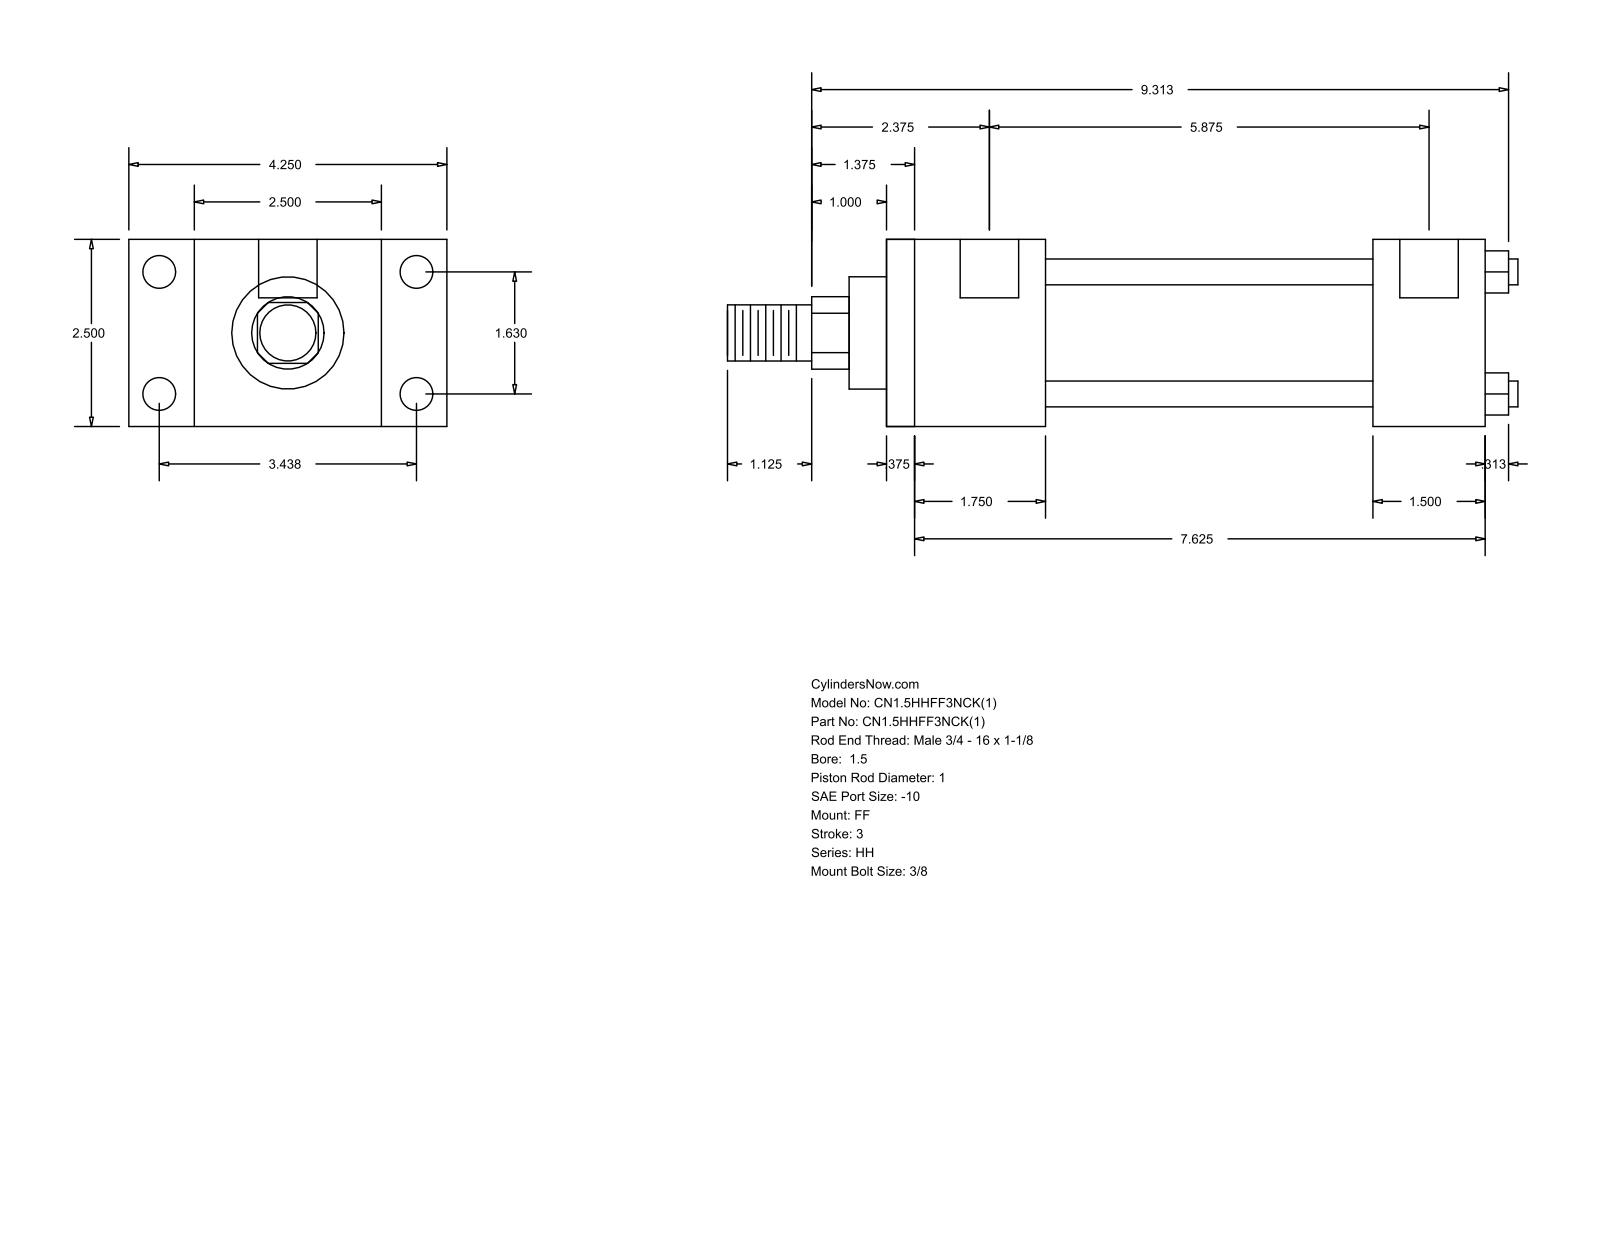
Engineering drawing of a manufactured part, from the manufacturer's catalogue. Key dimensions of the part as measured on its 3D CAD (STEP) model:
Part name (STEP PRODUCT): HH_FF__0150_1
STEP written by: GSSL Pune (CONFIG_CONTROL_DESIGN)
Units: millimetres
Bodies: 0 solids, 92 faces (64 planar, 28 cylindrical, 0 other)
Overall size (bounding box): 268.29 × 107.95 × 63.5
Round holes (diameter × count): ⌀5.56 ×4, ⌀11.13 ×4, ⌀19.84 ×2
Round bosses / shafts (diameter × count): ⌀8.76 ×4, ⌀44.45 ×1, ⌀38.1 ×1, ⌀25.4 ×1, ⌀19.05 ×1
Partial cylindrical surfaces — rounded edges, fillets, slot ends (radius × count): R12.29 ×1
Main face-to-face distances: 63.5, 203.2, 9.52, 193.68, 38.1, 53.98, 44.46, 149.22, 165.1, 155.58
Hole centre spacings: 1.59, 41.4, 87.32, 96.64, 150.81, 152.4, 149.22
